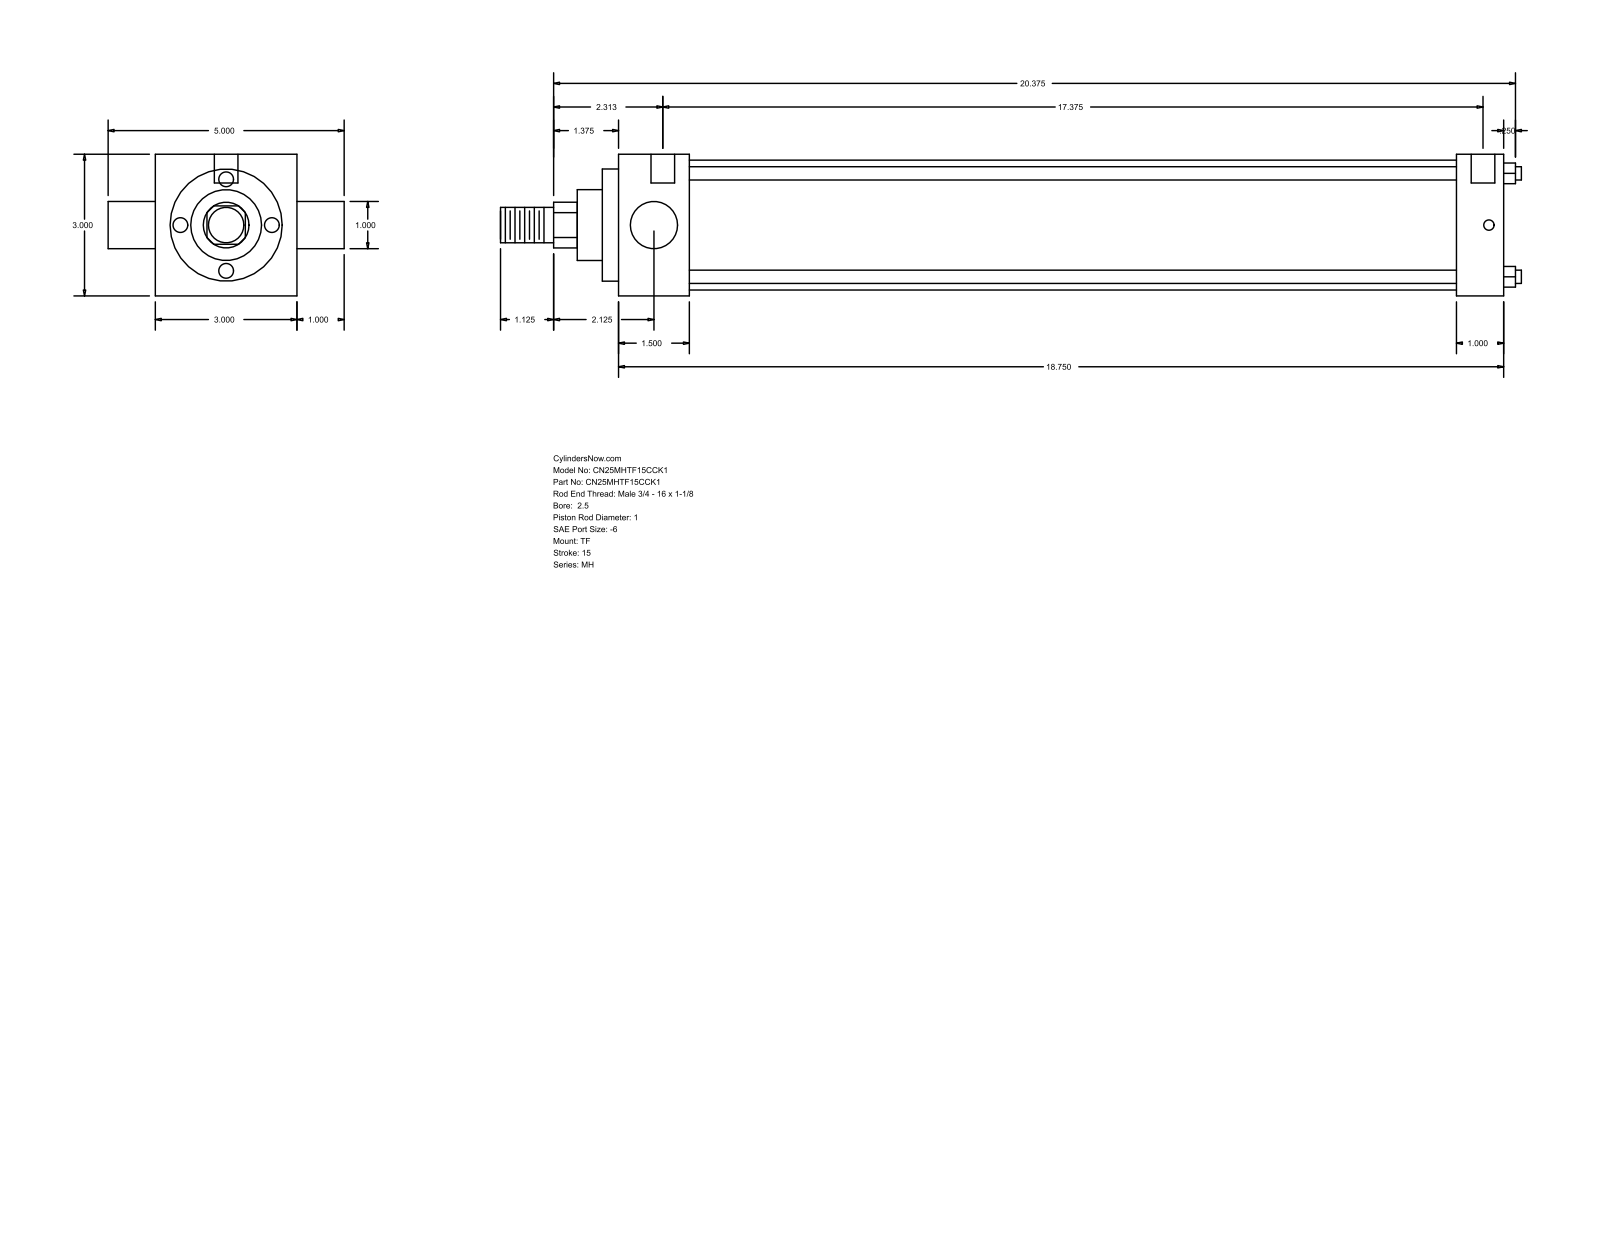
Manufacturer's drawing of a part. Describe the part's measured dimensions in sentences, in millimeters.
The part is named "MH_TF__0250_1". Its 3-D file was written by "GSSL Pune (CONFIG_CONTROL_DESIGN)". It is 0 solids with 86 faces: 61 planar, 25 cylindrical and 0 other. Overall it measures 549.27 by 127 by 76.2 millimeters. Round holes: 3 of diameter 5.56, 2 of diameter 12.7. Round bosses or shafts: 4 of diameter 7.14, 2 of diameter 25.4, 1 of diameter 69.85, 1 of diameter 60.33, 1 of diameter 38.1, 1 of diameter 19.05. Partial cylindrical surfaces (rounded edges, fillets, slot ends): 1 of radius 12.29. The main face-to-face distances are 76.2, 476.26, 38.11, 438.15, 450.85, 412.74, 25.41, 8.73, 46.84, 459.58. The hole center spacings are 3.18, 4.76, 441.32, 444.5, 446.08, 449.26.
